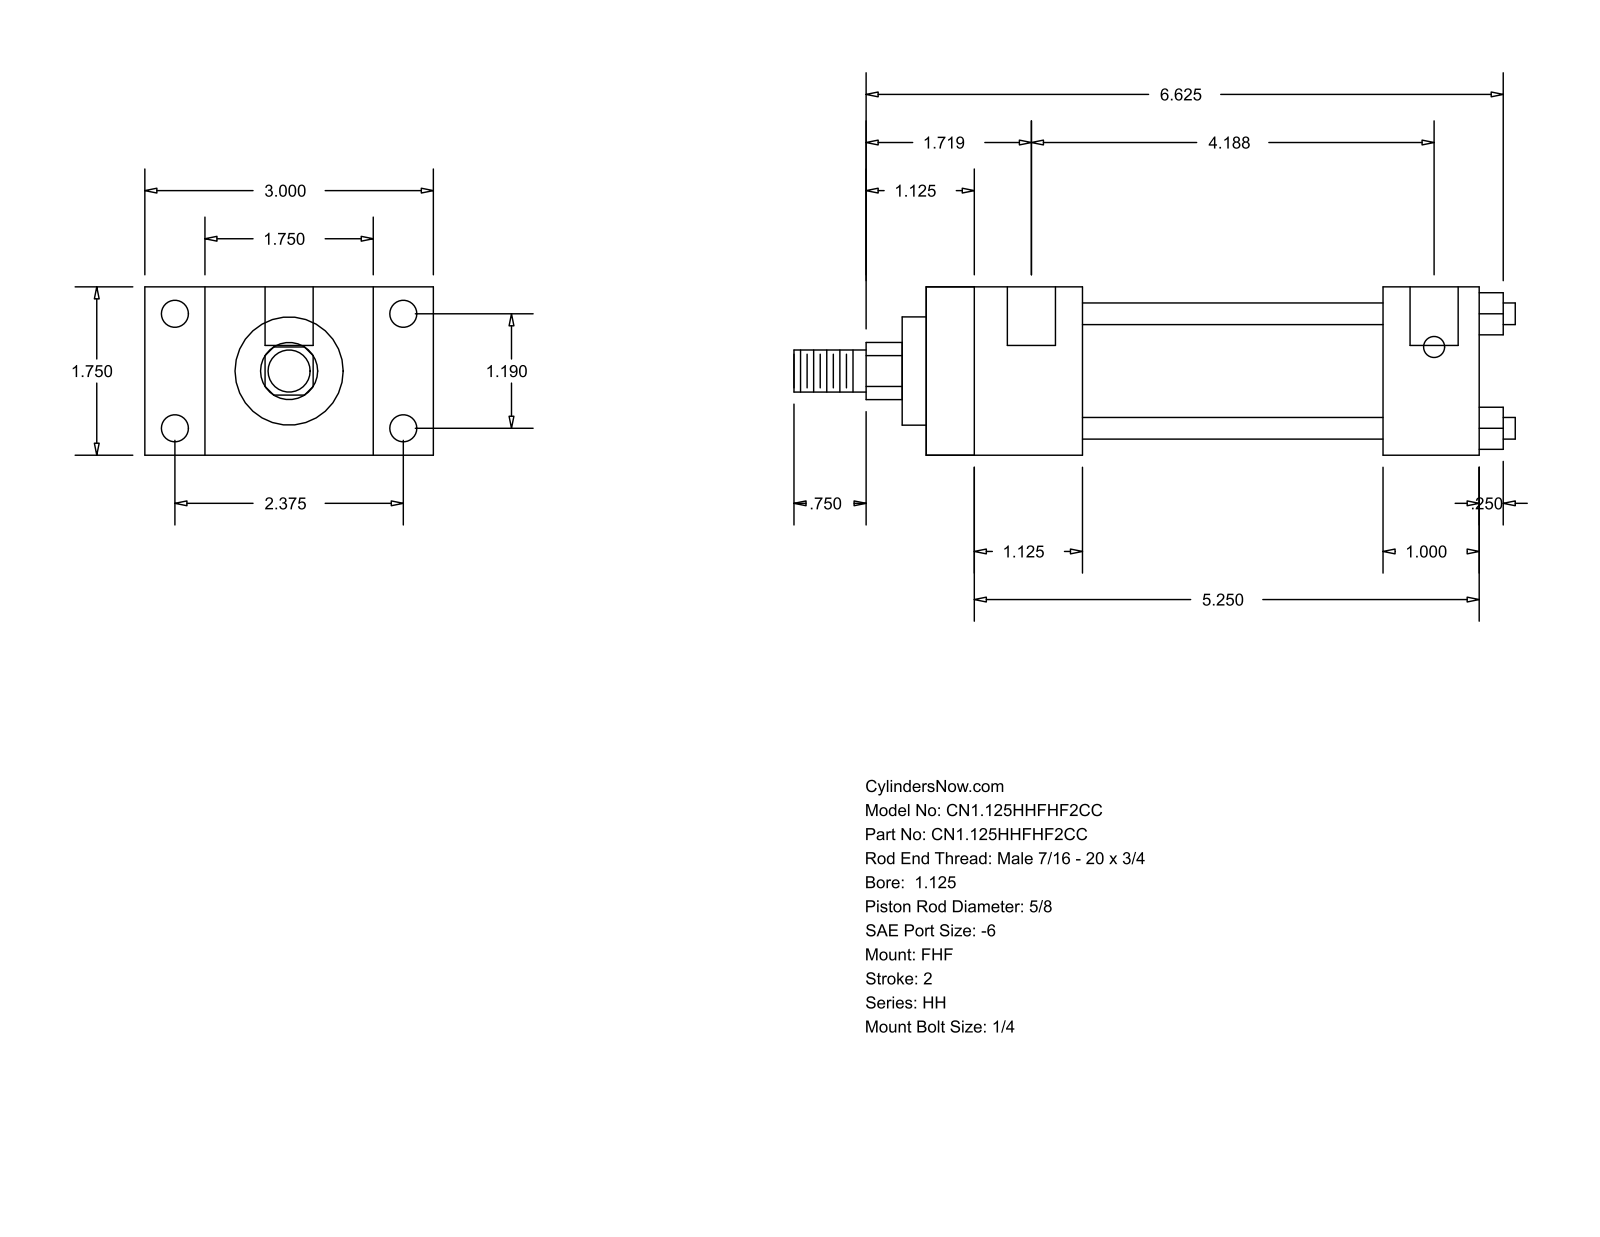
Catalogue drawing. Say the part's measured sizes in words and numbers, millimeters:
The part is named "HH_FHF__0112_0.625". Its 3-D file was written by "GSSL Pune (CONFIG_CONTROL_DESIGN)". It is 0 solids with 88 faces: 60 planar, 28 cylindrical and 0 other. Overall it measures 190.5 by 76.2 by 44.45 millimeters. Round holes: 4 of diameter 5.56, 4 of diameter 7.14, 2 of diameter 12.7. Round bosses or shafts: 4 of diameter 5.71, 1 of diameter 34.92, 1 of diameter 28.57, 1 of diameter 15.88, 1 of diameter 11.11. Partial cylindrical surfaces (rounded edges, fillets, slot ends): 1 of radius 7.54. The main face-to-face distances are 44.46, 15.87, 60.33, 41.27, 76.2, 146.05, 104.78, 25.4, 120.65, 79.38. The hole center spacings are 30.22, 60.32, 67.47, 103.19, 3.17, 106.36.
